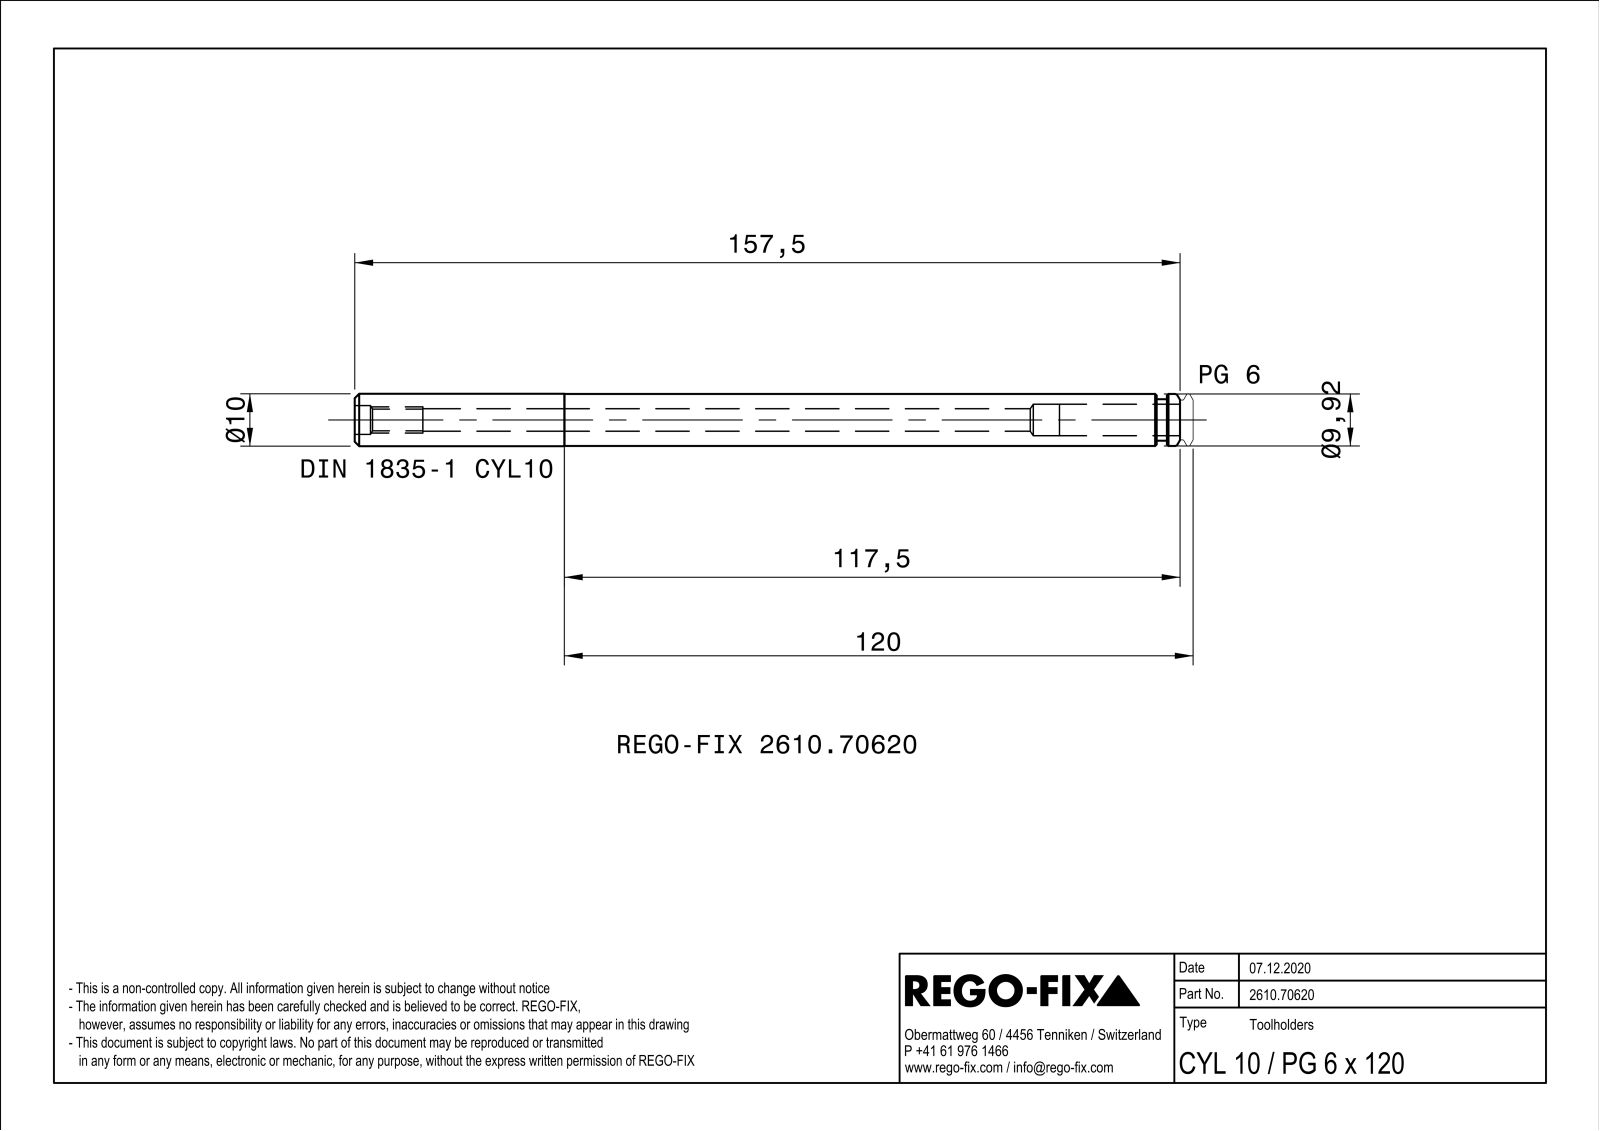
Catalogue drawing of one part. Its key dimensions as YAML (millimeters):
part_name: "NOCUT"
step_written_by: "SIEMENS PLM Software Solid Edge ST10 (AUTOMOTIVE_DESIGN)"
units: millimeters
bodies: {solids: 1, faces: 27, planar: 6, cylindrical: 8, other: 13}
overall_size: [157.5, 10, 10]
volume: 9525
surface_area: 7362
round_holes:
  - {diameter: 4.13, count: 1}
  - {diameter: 4.3, count: 1}
  - {diameter: 5.5, count: 1}
  - {diameter: 6.3, count: 1}
round_bosses_or_shafts:
  - {diameter: 10, count: 1}
  - {diameter: 9.92, count: 1}
  - {diameter: 8, count: 1}
face_to_face_distances: [153.05, 1.95, 155, 2.5, 4.45, 157.5, 23, 20.5, 18.55, 134.5]
